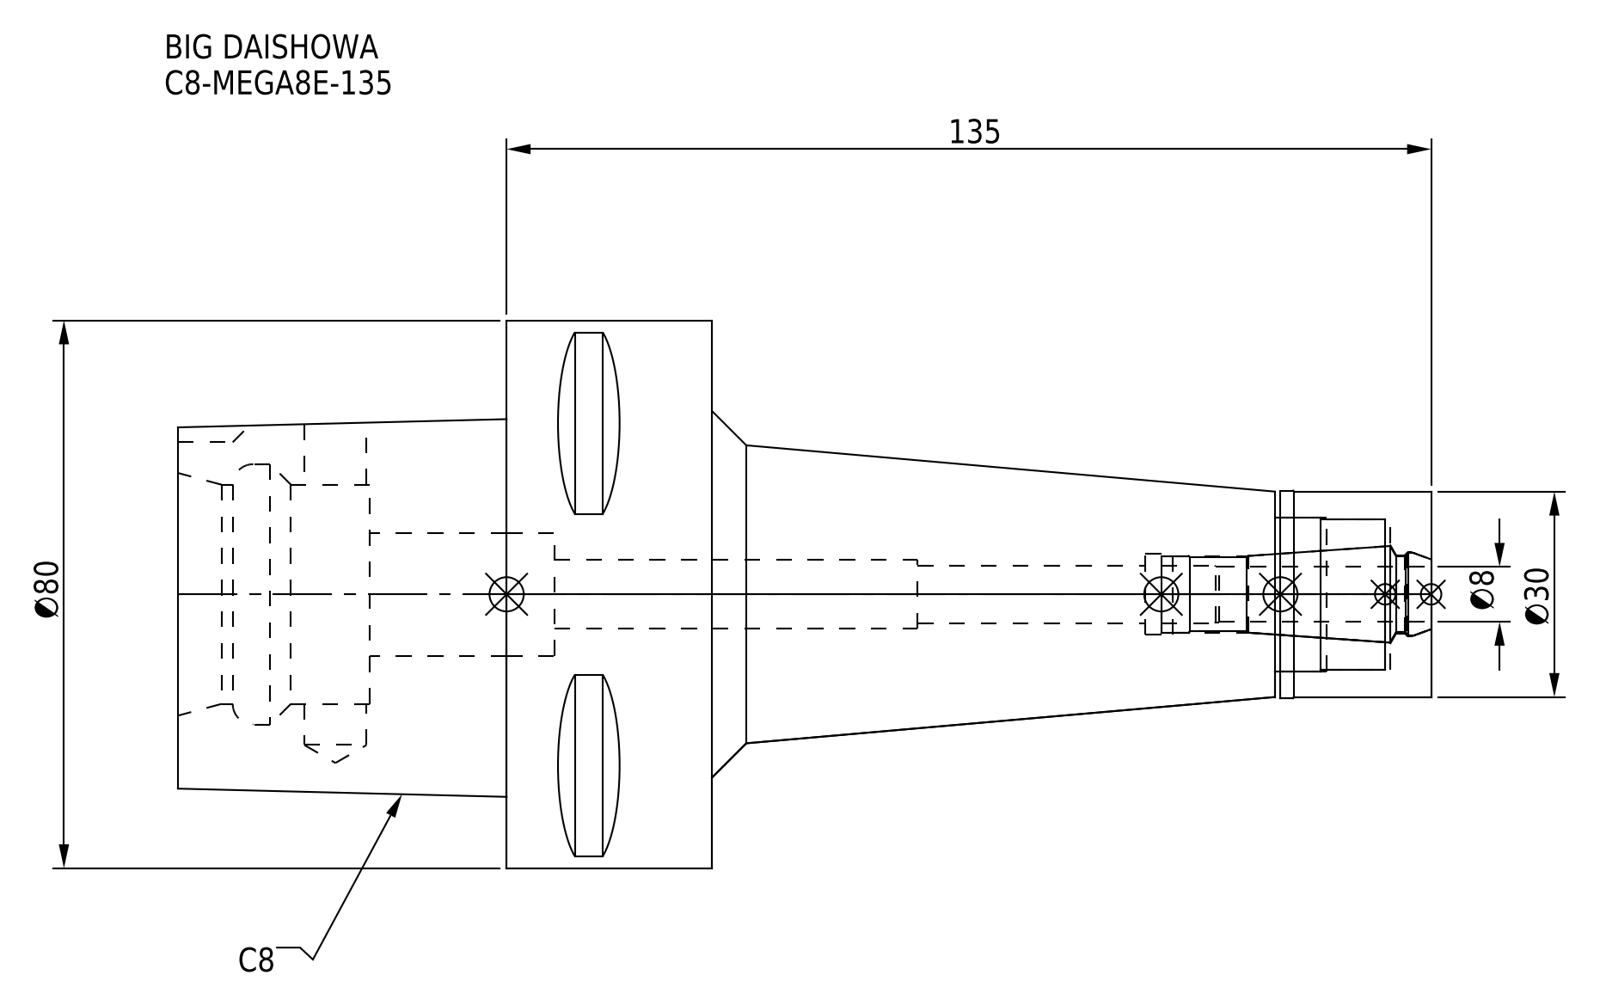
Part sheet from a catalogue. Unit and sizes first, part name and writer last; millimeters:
Units: millimetres
Overall size (bounding box): 183 × 80 × 80
Round holes (diameter × count): ⌀8.4 ×1, ⌀9.1 ×1, ⌀10 ×1, ⌀11.2 ×1, ⌀11.4 ×1, ⌀11.8 ×1, ⌀12.3 ×1, ⌀18 ×1, ⌀22 ×1, ⌀22.5 ×1, ⌀32 ×1, ⌀38 ×1
Round bosses / shafts (diameter × count): ⌀80 ×1, ⌀30.3 ×1, ⌀30 ×1
Partial cylindrical surfaces — rounded edges, fillets, slot ends (radius × count): R6 ×1
Main face-to-face distances: 30, 78, 48, 105, 135, 183, 20, 155, 50, 28
Volume: 320 204 mm³ · Surface area: 49 016 mm²
Bodies: 2 solids, 100 faces (37 planar, 39 cylindrical, 24 other)
Part name (STEP PRODUCT): C8-MEGA8E-135-080_ASM.stp; DXF_TEMP_ASSY_ASM_4_ASM.stp; C8-MEGA8E-135; C8-MEGA8E-135-080.stp (+3 more)
STEP written by: SolidWorks 2019 (CONFIG_CONTROL_DESIGN)
